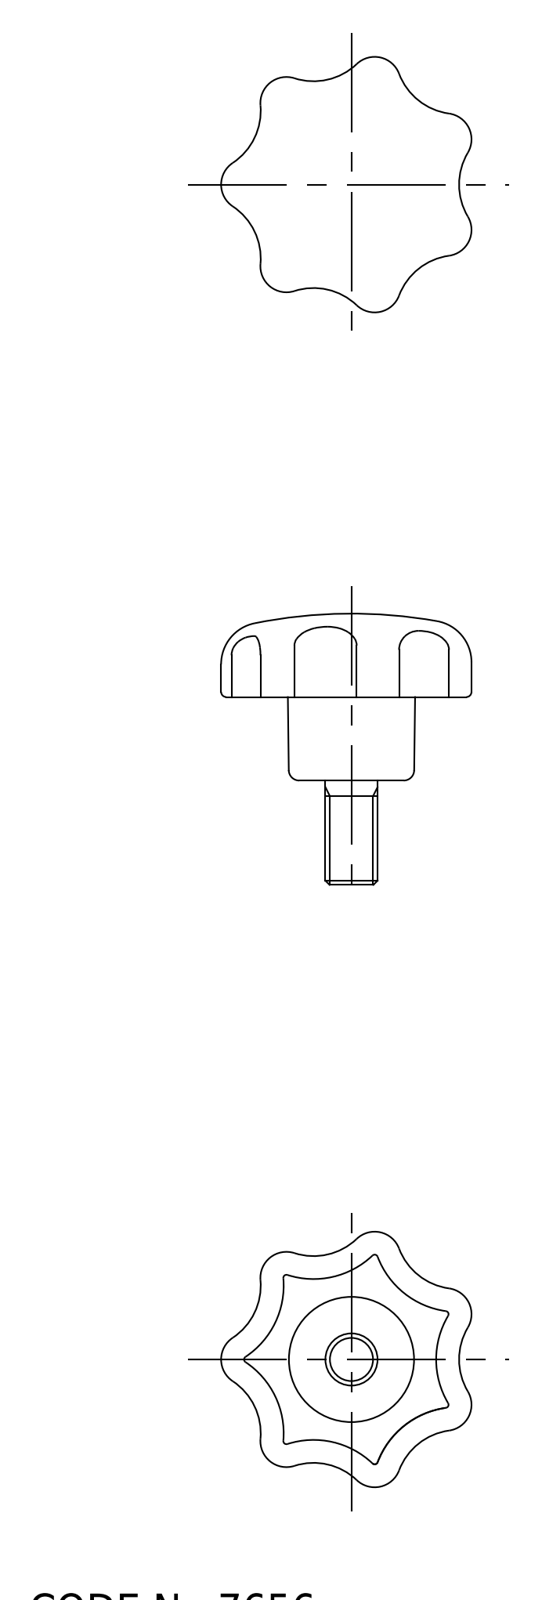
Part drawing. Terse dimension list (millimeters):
name: screw; knob; KSM_25_M5_10_8715_36
written by: CADfix (AUTOMOTIVE_DESIGN)
unit: mm
bodies: 2 solids, 125 faces (0 planar, 0 cylindrical, 125 other)
size: 26 × 24.5 × 24.01
volume: 3 346 mm³; area: 2 625 mm²
